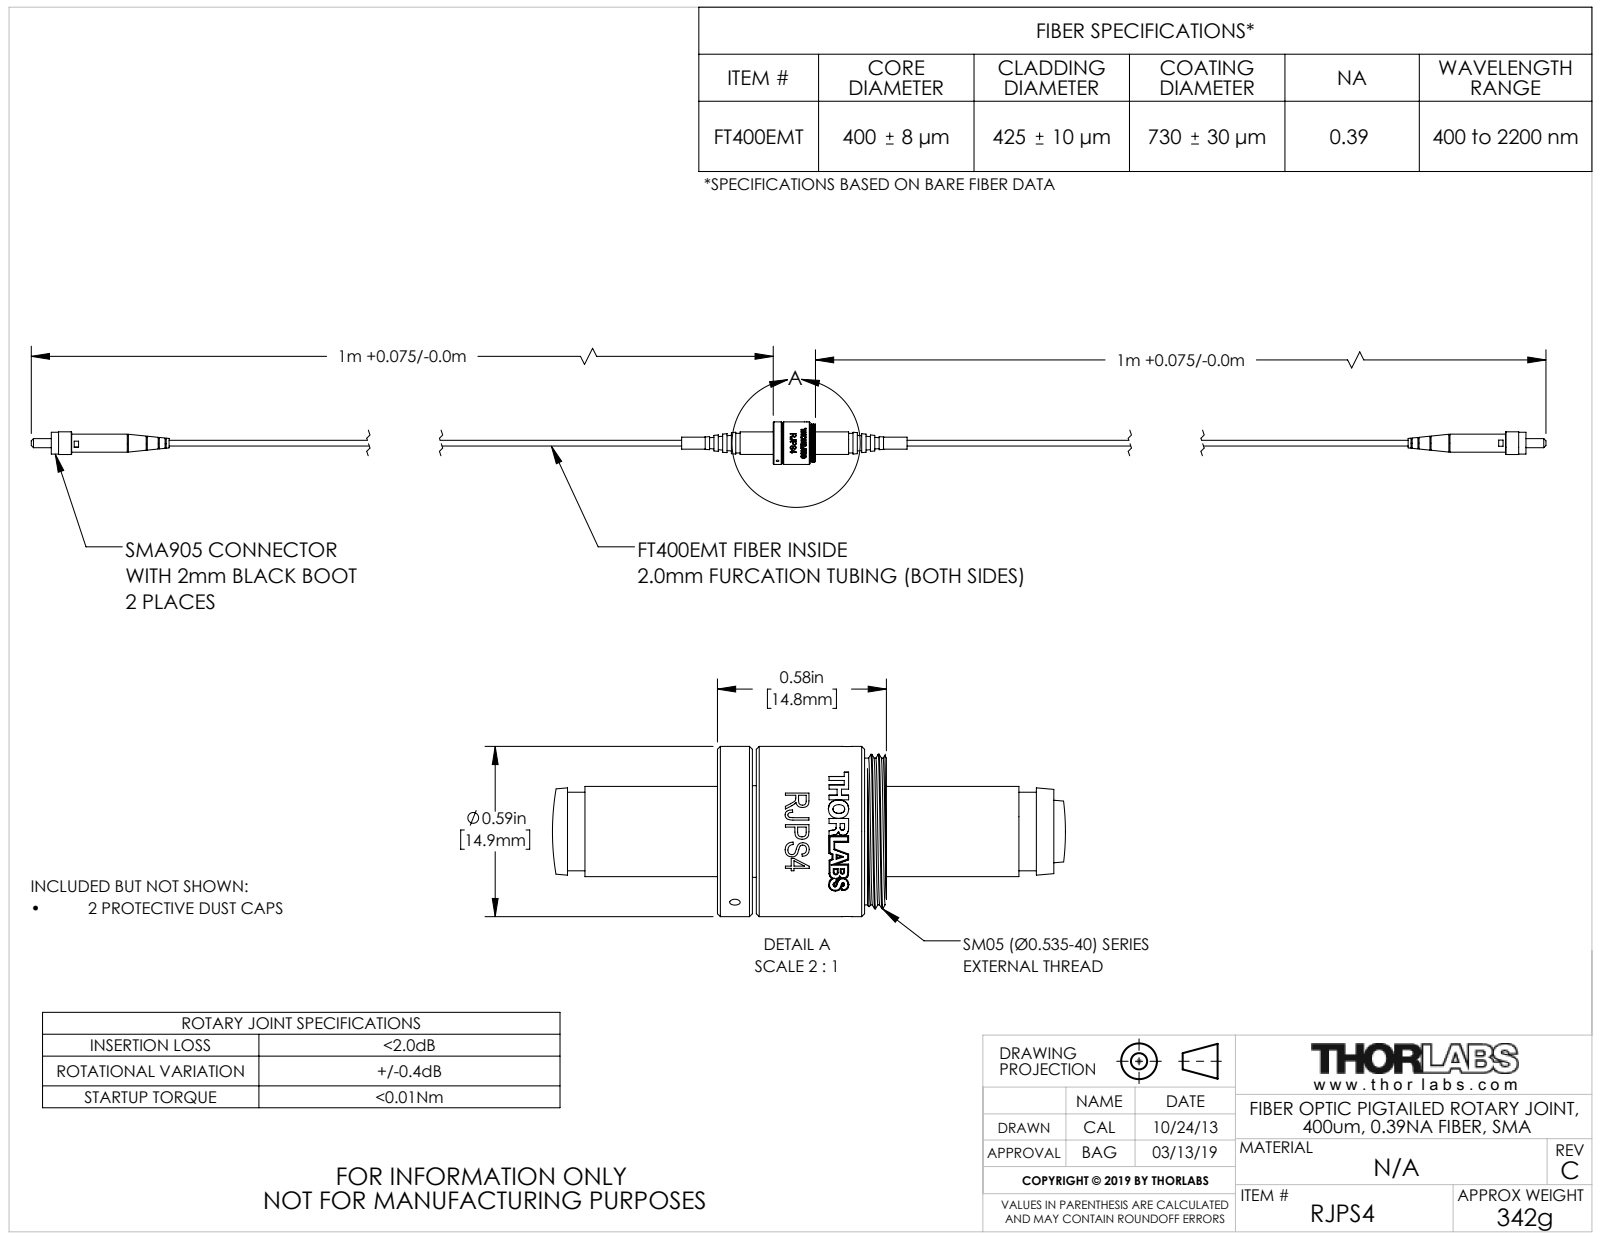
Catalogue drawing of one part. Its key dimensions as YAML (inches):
part_name: "TTN020011-E0W"
step_written_by: "SolidWorks 2012 (CONFIG_CONTROL_DESIGN)"
units: inches
bodies: {solids: 51, faces: 1189, planar: 291, cylindrical: 453, other: 445}
overall_size: [17.892, 1.907, 0.906]
volume: 0.699
surface_area: 35.29
round_holes:
  - {diameter: 0.036, count: 2}
  - {diameter: 0.009, count: 1}
  - {diameter: 0.009, count: 1}
  - {diameter: 0.085, count: 1}
  - {diameter: 0.085, count: 1}
  - {diameter: 0.09, count: 1}
  - {diameter: 0.098, count: 1}
  - {diameter: 0.1, count: 1}
  - {diameter: 0.141, count: 1}
  - {diameter: 0.155, count: 1}
  - {diameter: 0.183, count: 1}
  - {diameter: 0.19, count: 1}
round_bosses_or_shafts:
  - {diameter: 0.079, count: 3}
  - {diameter: 0.585, count: 1}
  - {diameter: 0.531, count: 1}
  - {diameter: 0.504, count: 1}
  - {diameter: 0.433, count: 1}
  - {diameter: 0.429, count: 1}
  - {diameter: 0.406, count: 1}
  - {diameter: 0.397, count: 1}
partial_cylinders:
  - {radius: 0.016, count: 36}
  - {radius: 0.023, count: 18}
  - {radius: 0.292, count: 1}
face_to_face_distances: [0.581, 0.118, 0.461, 0.12, 0.447, 0.013, 0.133, 0.254, 0.126, 8.101]
hole_center_spacings: [0.385]
